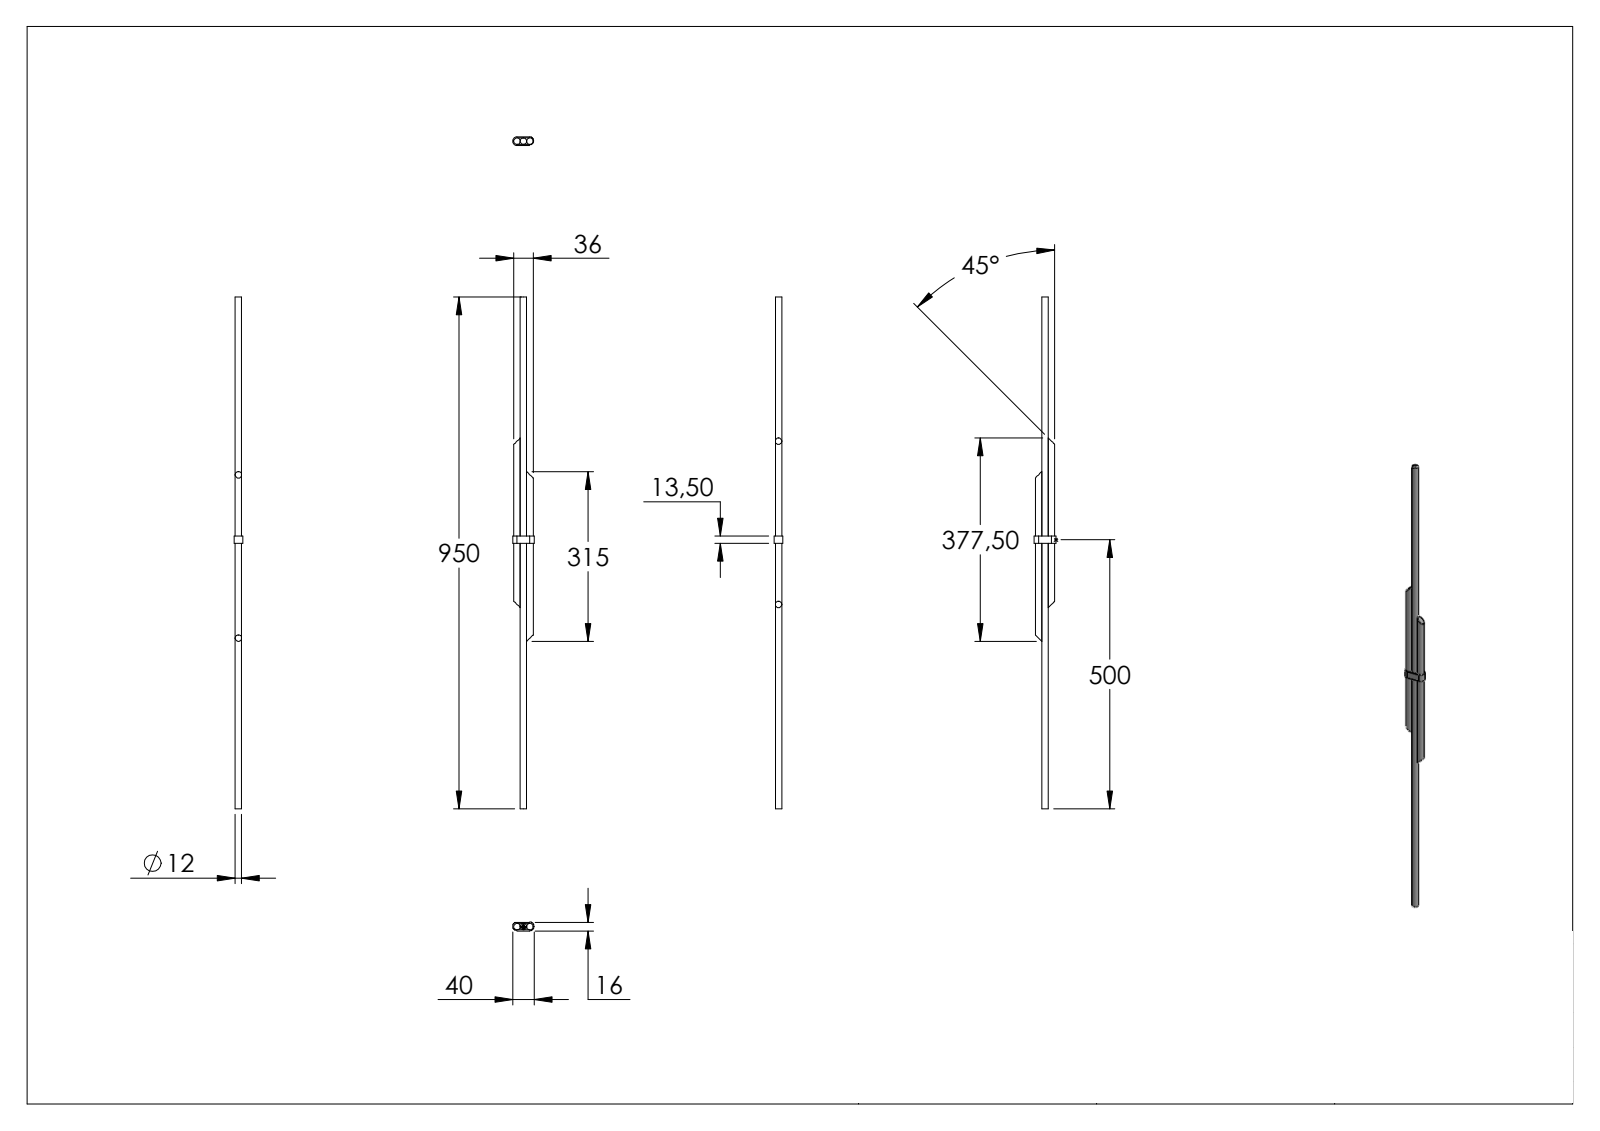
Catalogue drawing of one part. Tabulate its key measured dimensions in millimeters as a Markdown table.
| quantity | value |
| --- | --- |
| part name | 56124-240 |
| STEP written by | SolidWorks 2018 (CONFIG_CONTROL_DESIGN) |
| units | millimeters |
| bodies | 2 solids, 279 faces (168 planar, 5 cylindrical, 106 other) |
| overall size | 950 × 40 × 16 |
| volume | 178 522 mm³ |
| surface area | 61 368 mm² |
| round bosses / shafts (diameter × count) | 12 × 3 |
| partial cylindrical surfaces (radius × count) | 8 × 2 |
| main face-to-face distances | 2, 14, 12, 16, 13.5, 275.38, 187, 493.25, 506.75, 950 |
